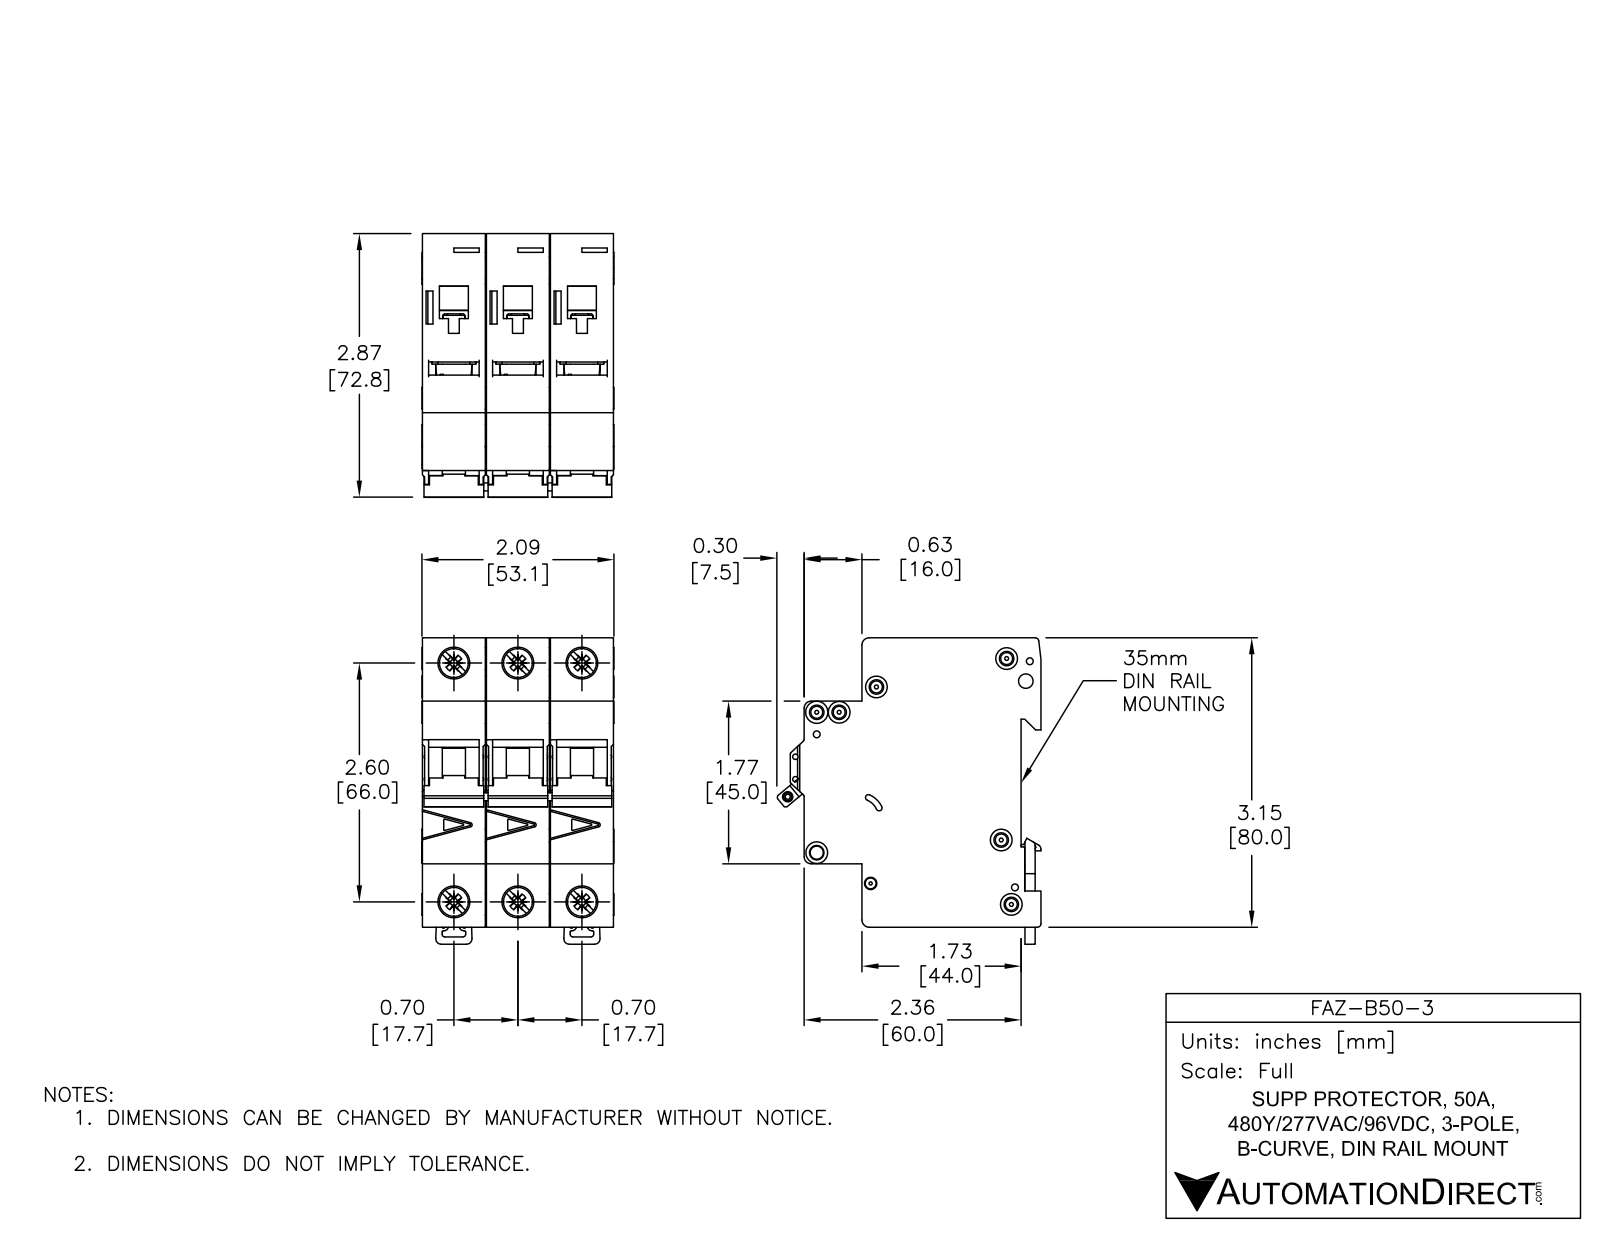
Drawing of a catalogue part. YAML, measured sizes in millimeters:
part_name: "FAZ-B50-3"
step_written_by: "SolidWorks 2014 (AUTOMOTIVE_DESIGN)"
units: millimeters
bodies: {solids: 11, faces: 1650, planar: 697, cylindrical: 590, other: 363}
overall_size: [84.78, 73.04, 53.1]
volume: 224680
surface_area: 58052
round_holes:
  - {diameter: 3.6, count: 6}
  - {diameter: 8.2, count: 4}
  - {diameter: 1.9, count: 3}
  - {diameter: 1.09, count: 2}
  - {diameter: 1.5, count: 2}
  - {diameter: 4, count: 2}
  - {diameter: 7.15, count: 2}
  - {diameter: 2.15, count: 1}
  - {diameter: 2.2, count: 1}
  - {diameter: 2.55, count: 1}
  - {diameter: 3.3, count: 1}
  - {diameter: 3.4, count: 1}
round_bosses_or_shafts:
  - {diameter: 6, count: 4}
  - {diameter: 2.5, count: 3}
  - {diameter: 8.2, count: 2}
partial_cylinders:
  - {radius: 0.25, count: 68}
  - {radius: 0.5, count: 25}
  - {radius: 1, count: 12}
  - {radius: 2, count: 12}
  - {radius: 0.2, count: 11}
  - {radius: 1.8, count: 3}
  - {radius: 0.8, count: 2}
  - {radius: 3, count: 2}
face_to_face_distances: [17.7, 17.5, 35.4, 35.2, 52.9, 17.9, 79.48, 5.5, 49.5, 44]
hole_center_spacings: [17.7, 68.33, 66, 6.2, 13.64, 35.4, 74.89, 4.81]
